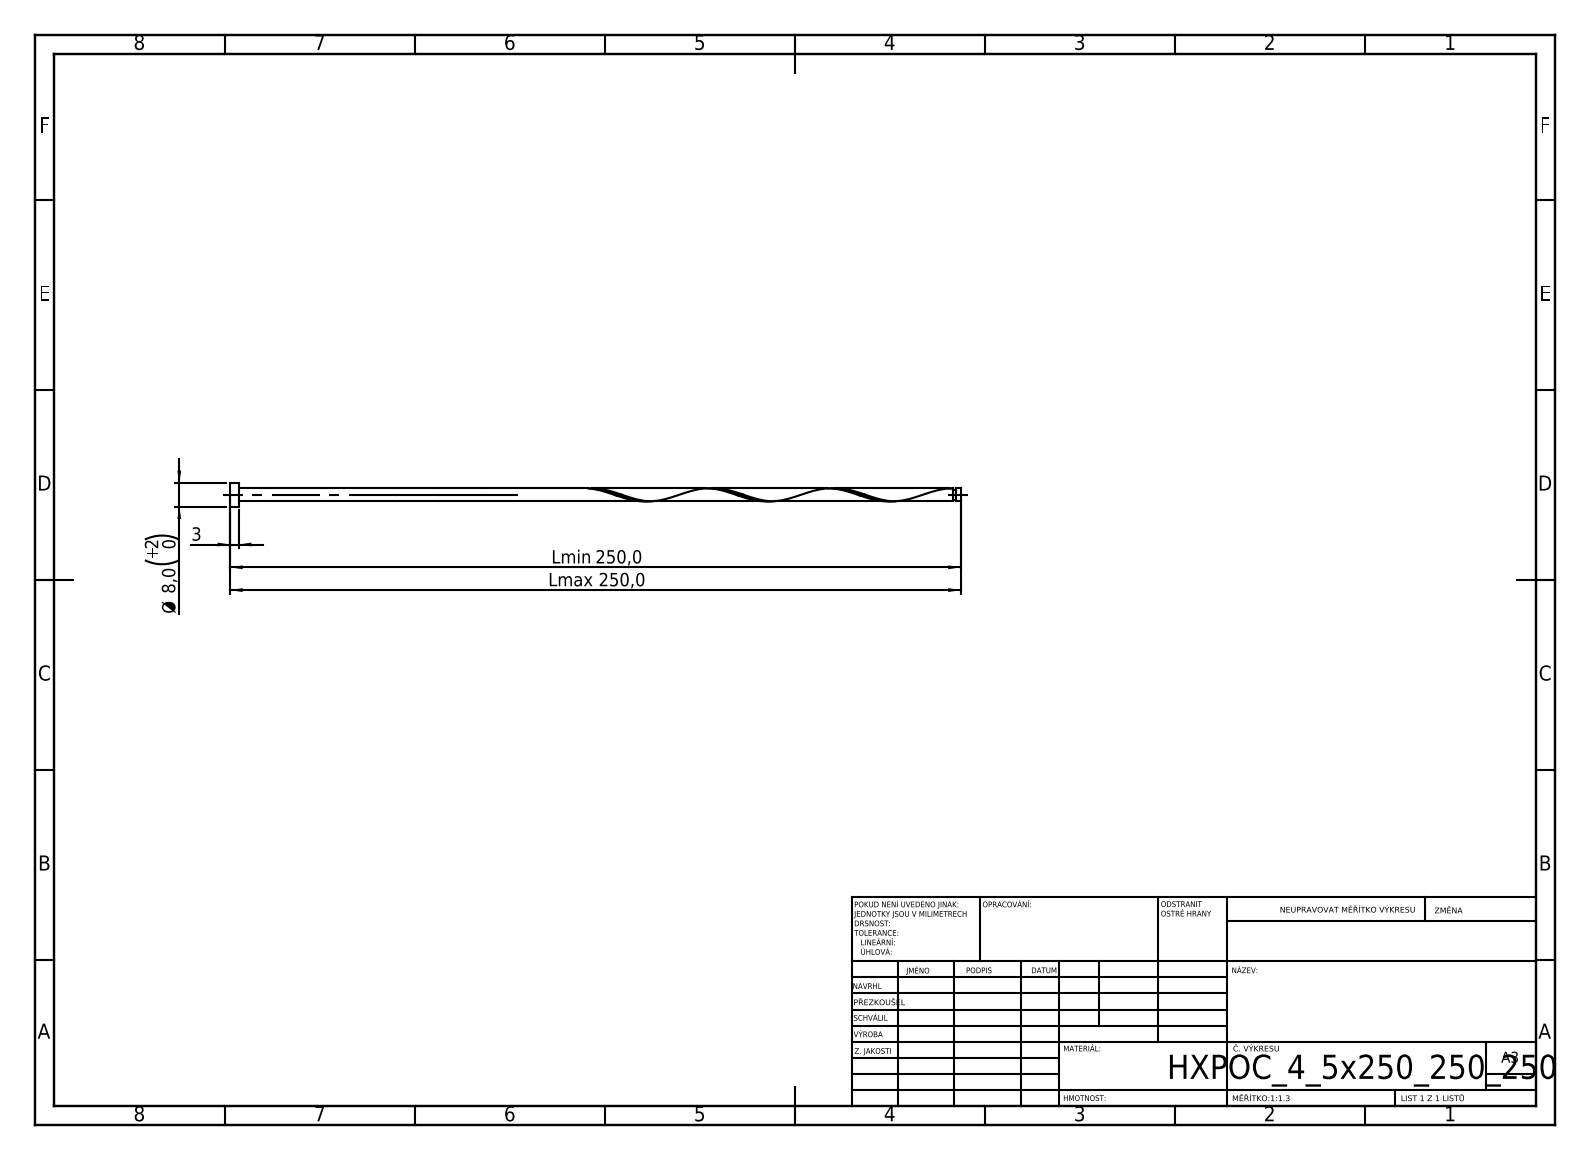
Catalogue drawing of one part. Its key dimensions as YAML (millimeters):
step_written_by: "SolidWorks 2019 (CONFIG_CONTROL_DESIGN)"
units: millimeters
bodies: {solids: 1, faces: 16, planar: 6, cylindrical: 9, other: 1}
overall_size: [250, 8, 8]
volume: 4920
surface_area: 4913
round_bosses_or_shafts:
  - {diameter: 8, count: 1}
  - {diameter: 4.5, count: 1}
  - {diameter: 3.6, count: 1}
face_to_face_distances: [3, 250, 247, 248.27, 245.27, 1.73, 247.37, 244.37, 0.9, 2.63]
